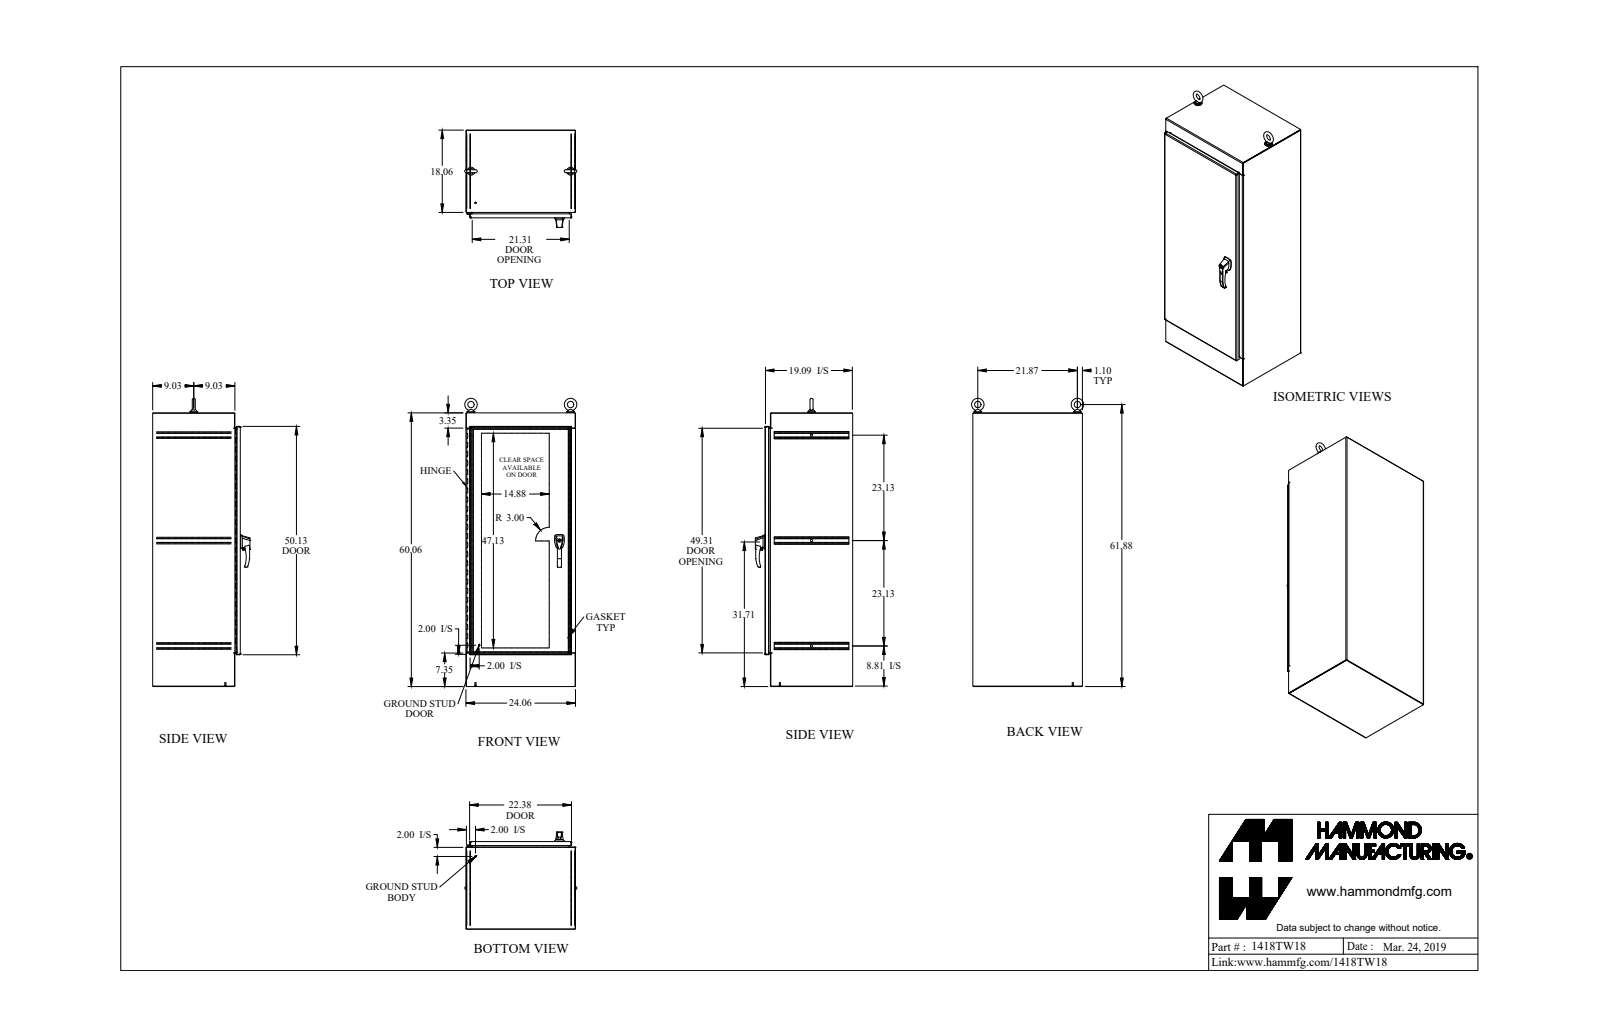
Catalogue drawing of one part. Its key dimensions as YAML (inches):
part_name: "1418TW18_Default"
step_written_by: "SolidWorks 2019 (CONFIG_CONTROL_DESIGN)"
units: inches
bodies: {solids: 54, faces: 2418, planar: 1057, cylindrical: 1062, other: 299}
overall_size: [63.713, 25.118, 21.363]
volume: 717.5
surface_area: 14976
round_holes:
  - {diameter: 0.304, count: 9}
  - {diameter: 0.35, count: 7}
  - {diameter: 0.75, count: 4}
  - {diameter: 0.5, count: 3}
  - {diameter: 0.25, count: 2}
  - {diameter: 0.257, count: 2}
  - {diameter: 0.28, count: 2}
  - {diameter: 0.281, count: 2}
  - {diameter: 0.313, count: 2}
  - {diameter: 0.39, count: 2}
  - {diameter: 0.413, count: 2}
  - {diameter: 0.527, count: 2}
round_bosses_or_shafts:
  - {diameter: 0.281, count: 4}
  - {diameter: 1.75, count: 2}
  - {diameter: 1.5, count: 2}
  - {diameter: 1.25, count: 2}
  - {diameter: 1, count: 2}
  - {diameter: 0.75, count: 2}
  - {diameter: 0.738, count: 2}
  - {diameter: 0.63, count: 2}
partial_cylinders:
  - {radius: 0.043, count: 42}
  - {radius: 0.138, count: 36}
  - {radius: 0.5, count: 25}
  - {radius: 0.125, count: 22}
  - {radius: 0.018, count: 16}
  - {radius: 0.06, count: 15}
  - {radius: 0.048, count: 14}
  - {radius: 0.143, count: 14}
face_to_face_distances: [0.095, 23.965, 0.095, 23.87, 19.057, 19.153, 19.152, 19.248, 24.06, 59.965]
hole_center_spacings: [6, 12, 18, 24, 21.87, 30, 36, 0.03]
